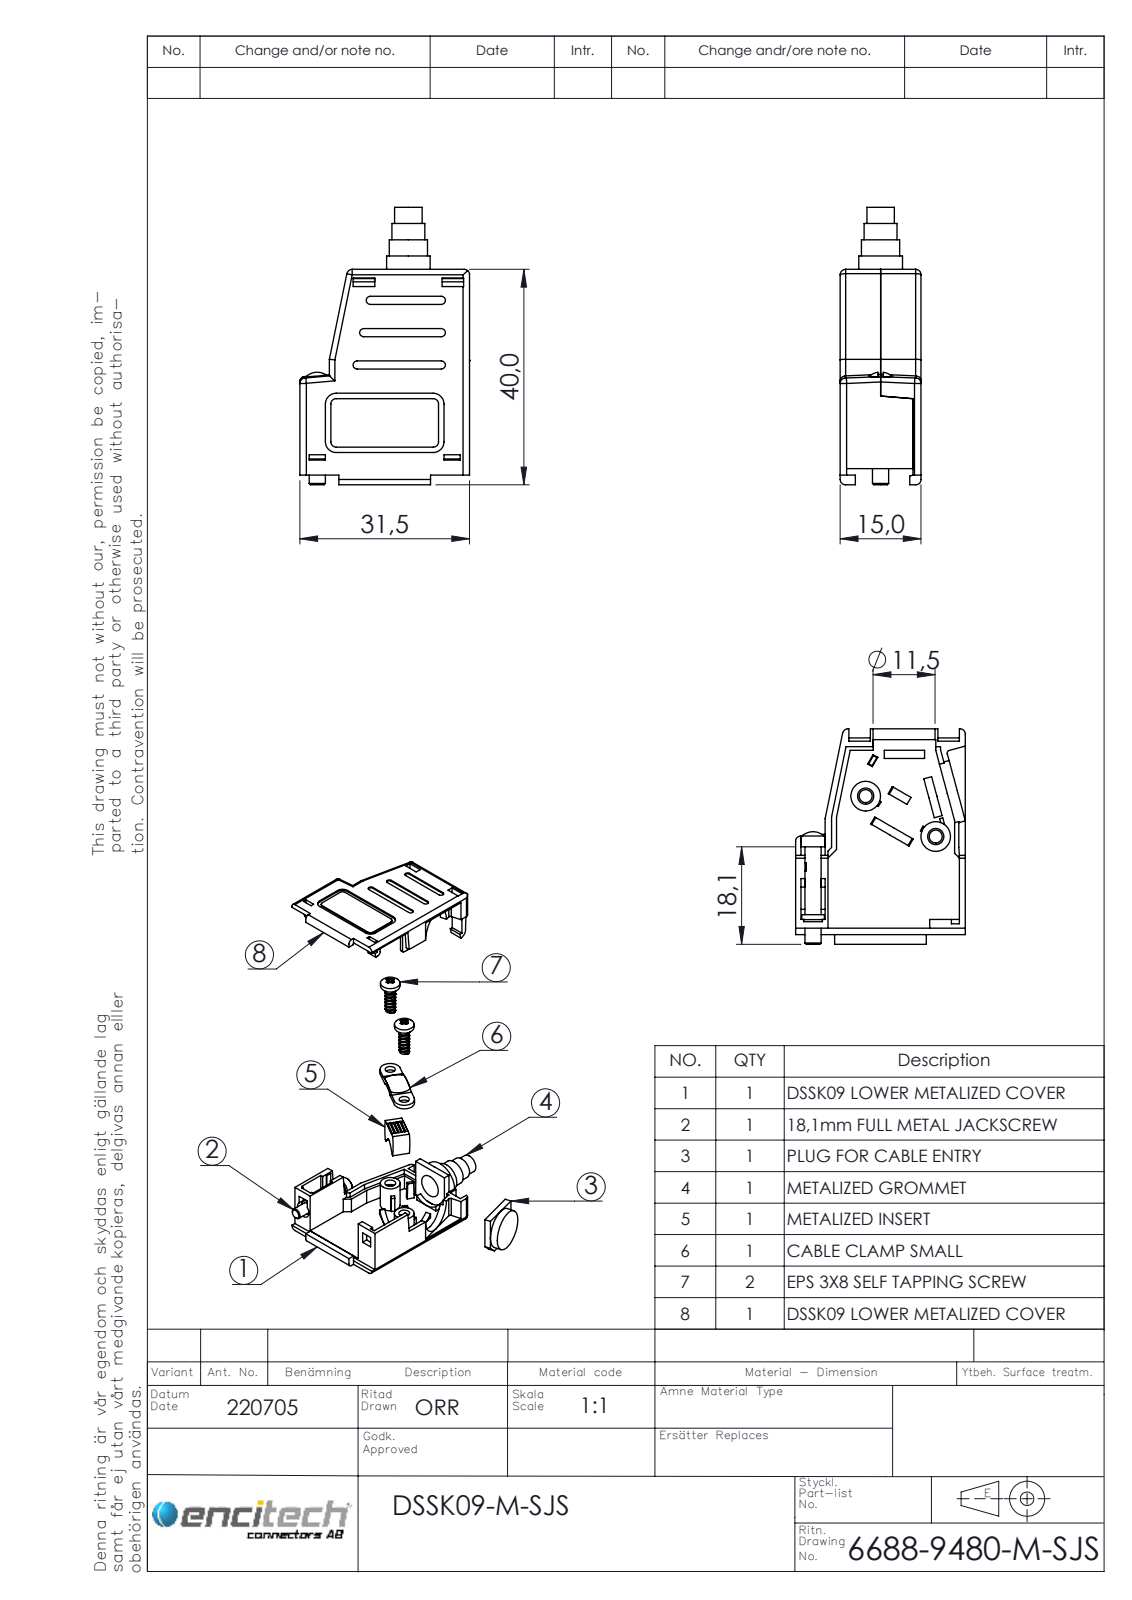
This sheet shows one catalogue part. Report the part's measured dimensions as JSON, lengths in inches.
{"part_name": "6811-0141-03 Part 1; 6822-0128-32; 6688-9480-M-SJS; 6830-0106-01 (+5 more)", "step_written_by": "SolidWorks 2021 (AUTOMOTIVE_DESIGN)", "units": "inches", "bodies": {"solids": 11, "faces": 686, "planar": 457, "cylindrical": 182, "other": 47}, "overall_size": [2.028, 1.243, 0.591], "volume_in3": 0.443, "surface_area_in2": 17.3, "round_holes": [[0.094, 2], [0.11, 2], [0.118, 2], [0.138, 2], [0.177, 2], [0.217, 1], [0.256, 1], [0.37, 1], [0.453, 1], [0.457, 1]], "round_bosses_or_shafts": [[0.217, 2], [0.215, 2], [0.097, 2], [0.449, 1], [0.445, 1], [0.319, 1], [0.28, 1], [0.24, 1]], "partial_cylinders_radius": [[0.039, 20], [0.02, 6], [0.03, 6], [0.079, 6], [0.047, 4], [0.004, 2], [0.112, 2], [0.512, 2]], "face_to_face_distances": [0.524, 0.067, 0.059, 0.457, 0.591, 0.516, 0.079, 0.063, 0.047, 0.295], "hole_center_spacings": [0.295, 0.591, 0.665]}
